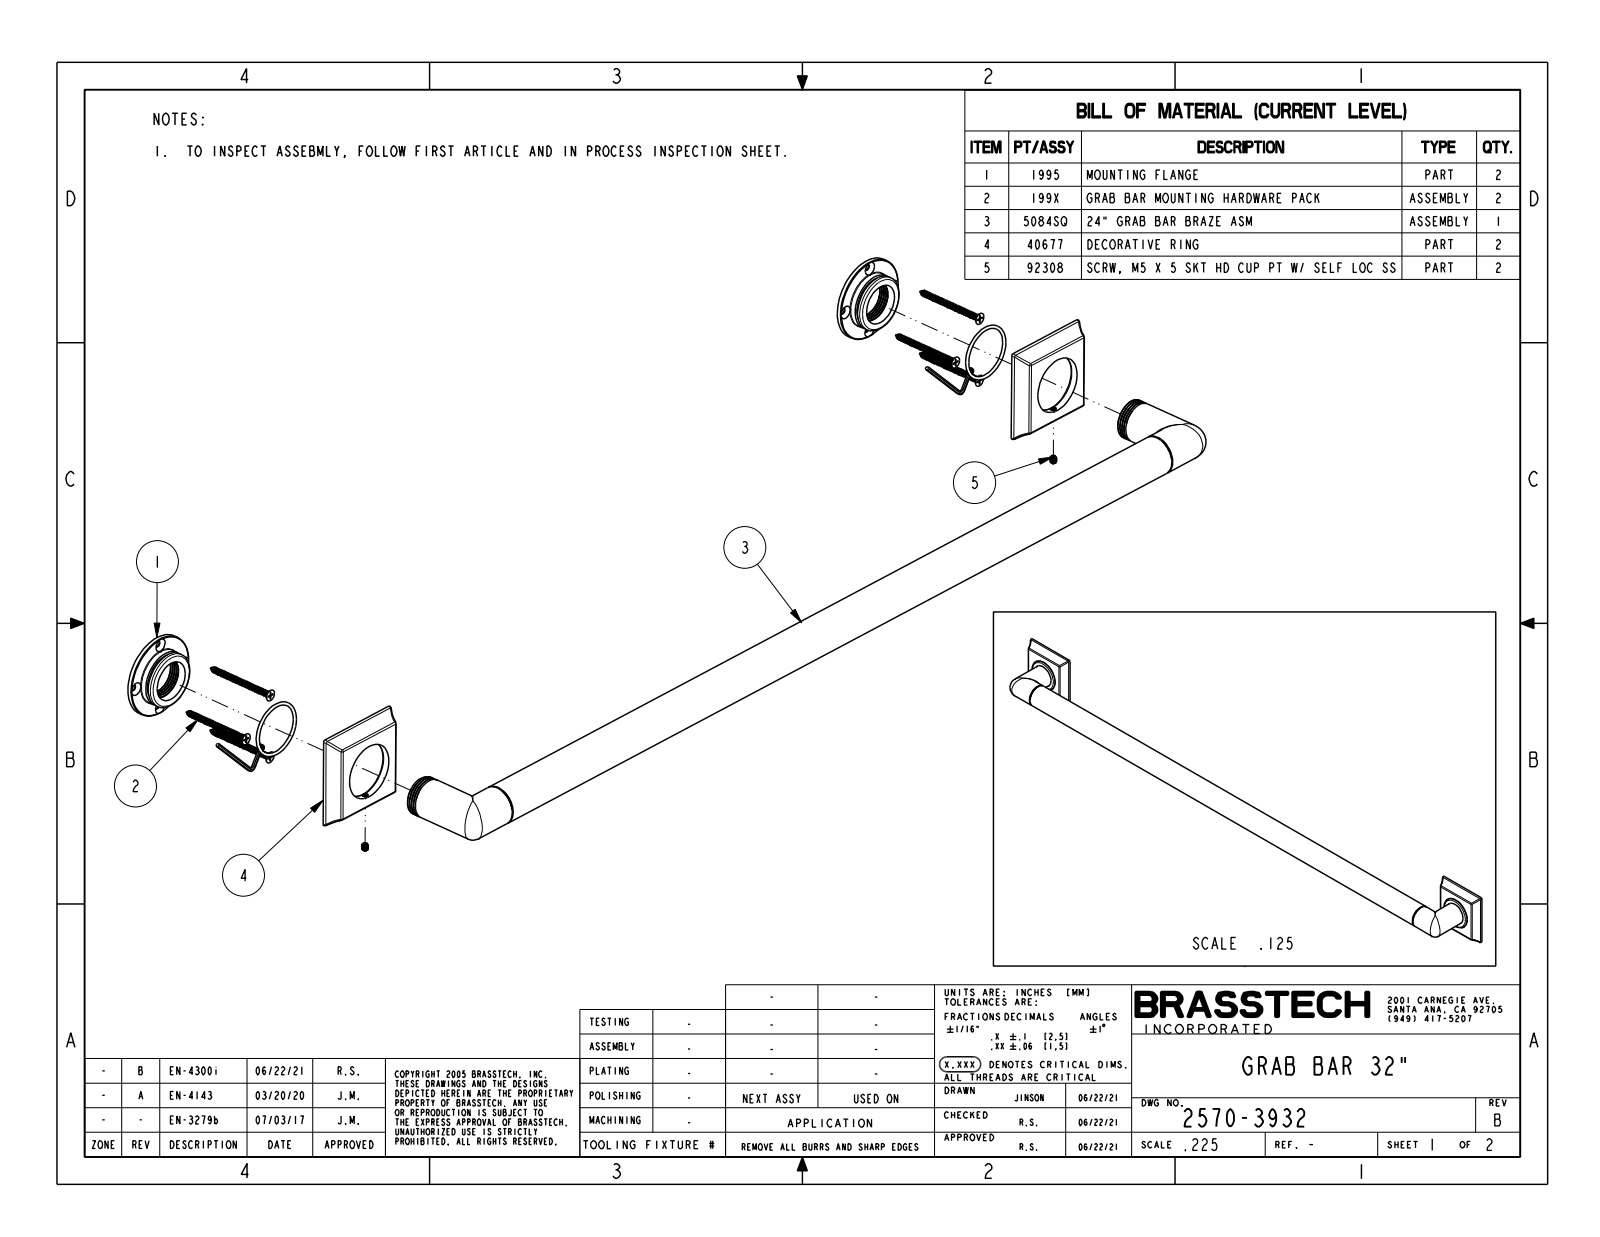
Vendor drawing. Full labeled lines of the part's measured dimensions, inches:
Part name (STEP PRODUCT): 2570-3932
STEP written by: CREO PARAMETRIC BY PTC INC, 2018400 (CONFIG_CONTROL_DESIGN)
Units: inches
Bodies: 1 solid, 88 faces (6 planar, 38 cylindrical, 44 other)
Overall size (bounding box): 35 × 3 × 2.755
Volume: 51.04 in³ · Surface area: 178.2 in²
Round bosses / shafts (diameter × count): ⌀1.25 ×3, ⌀1.75 ×2
Partial cylindrical surfaces — rounded edges, fillets, slot ends (radius × count): R0.06 ×6, R0.125 ×6, R1.35 ×6
Main face-to-face distances: 0.525, 0.6, 0.075
